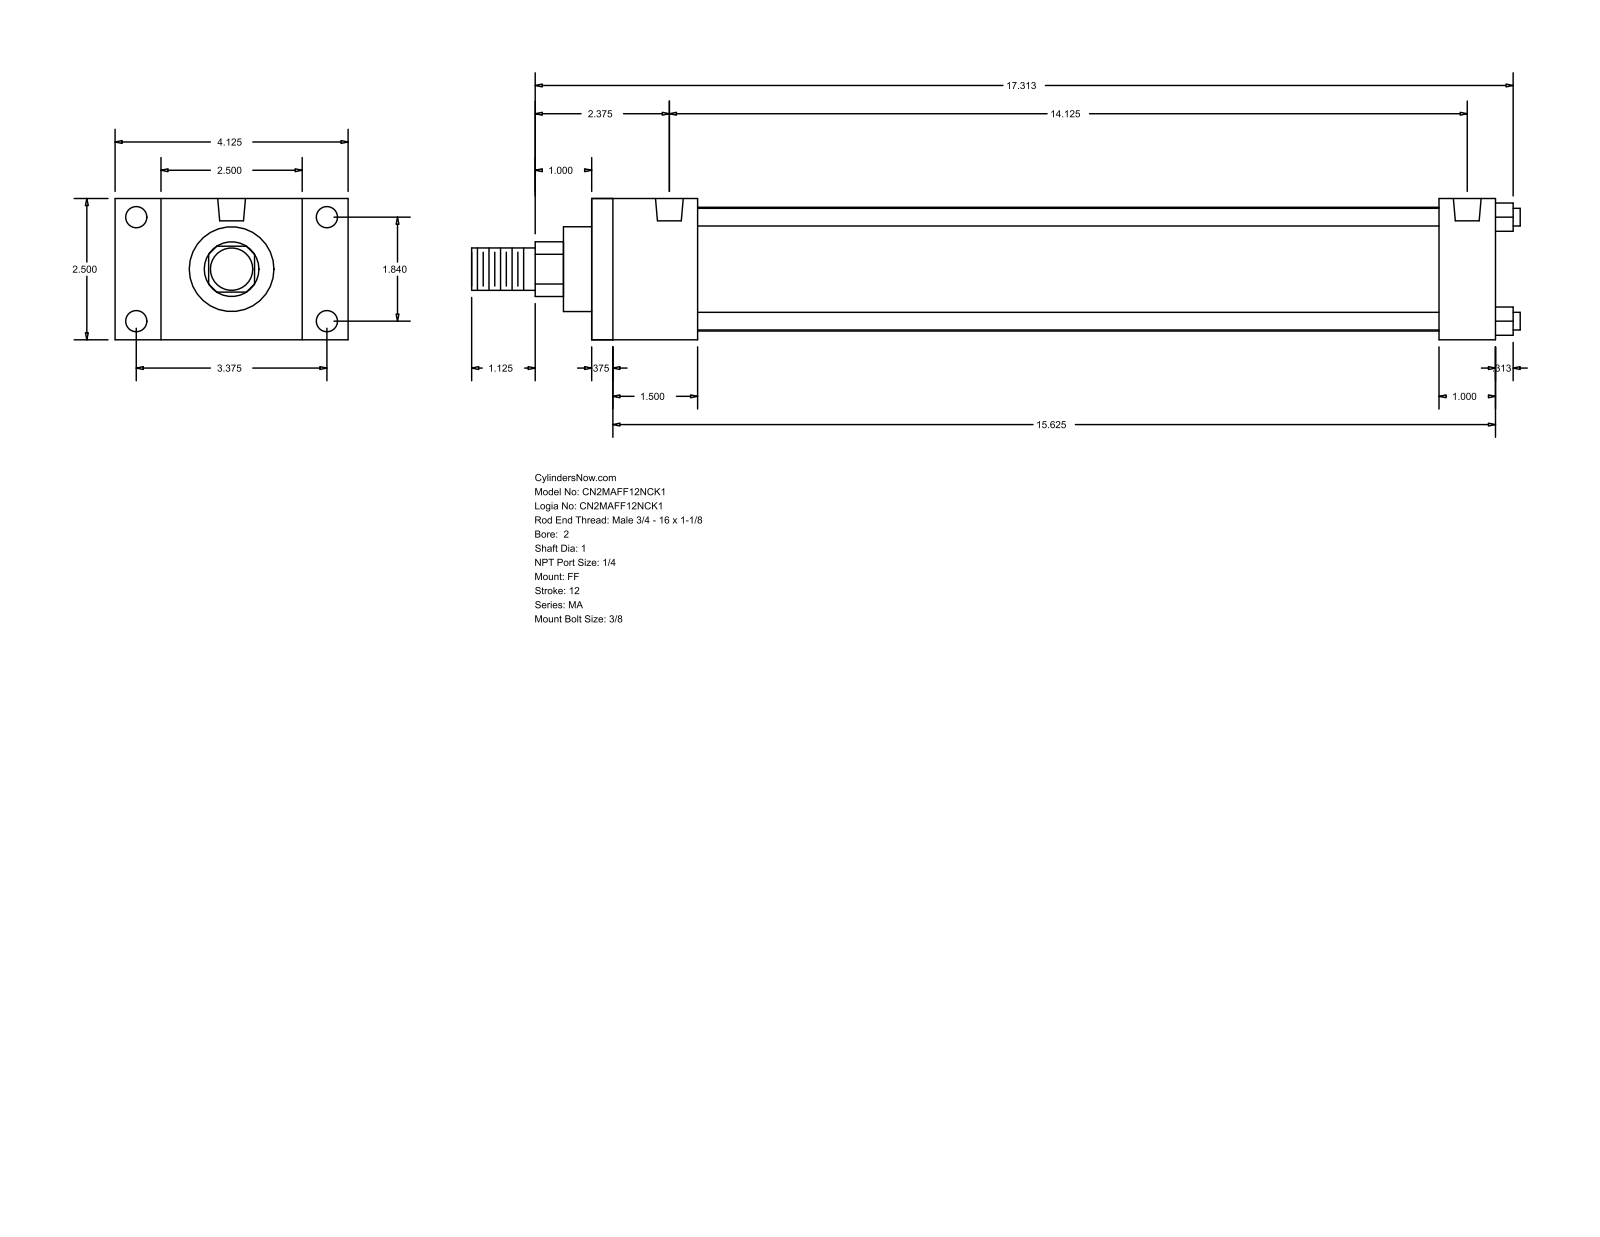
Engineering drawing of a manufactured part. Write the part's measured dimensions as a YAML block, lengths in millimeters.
part_name: "MA_FF__0200_1"
step_written_by: "GSSL Pune (CONFIG_CONTROL_DESIGN)"
units: millimeters
bodies: {solids: 0, faces: 92, planar: 64, cylindrical: 28, other: 0}
overall_size: [471.49, 104.78, 63.5]
round_holes:
  - {diameter: 7.94, count: 4}
  - {diameter: 9.53, count: 4}
  - {diameter: 12.49, count: 2}
round_bosses_or_shafts:
  - {diameter: 7.94, count: 4}
  - {diameter: 55.63, count: 1}
  - {diameter: 38.1, count: 1}
  - {diameter: 25.4, count: 1}
  - {diameter: 19.05, count: 1}
partial_cylinders:
  - {radius: 12.29, count: 1}
face_to_face_distances: [63.5, 406.4, 9.52, 396.88, 25.4, 20.64, 12.7, 47.63, 381, 38.11]
hole_center_spacings: [46.74, 85.72, 97.63, 358.77]
